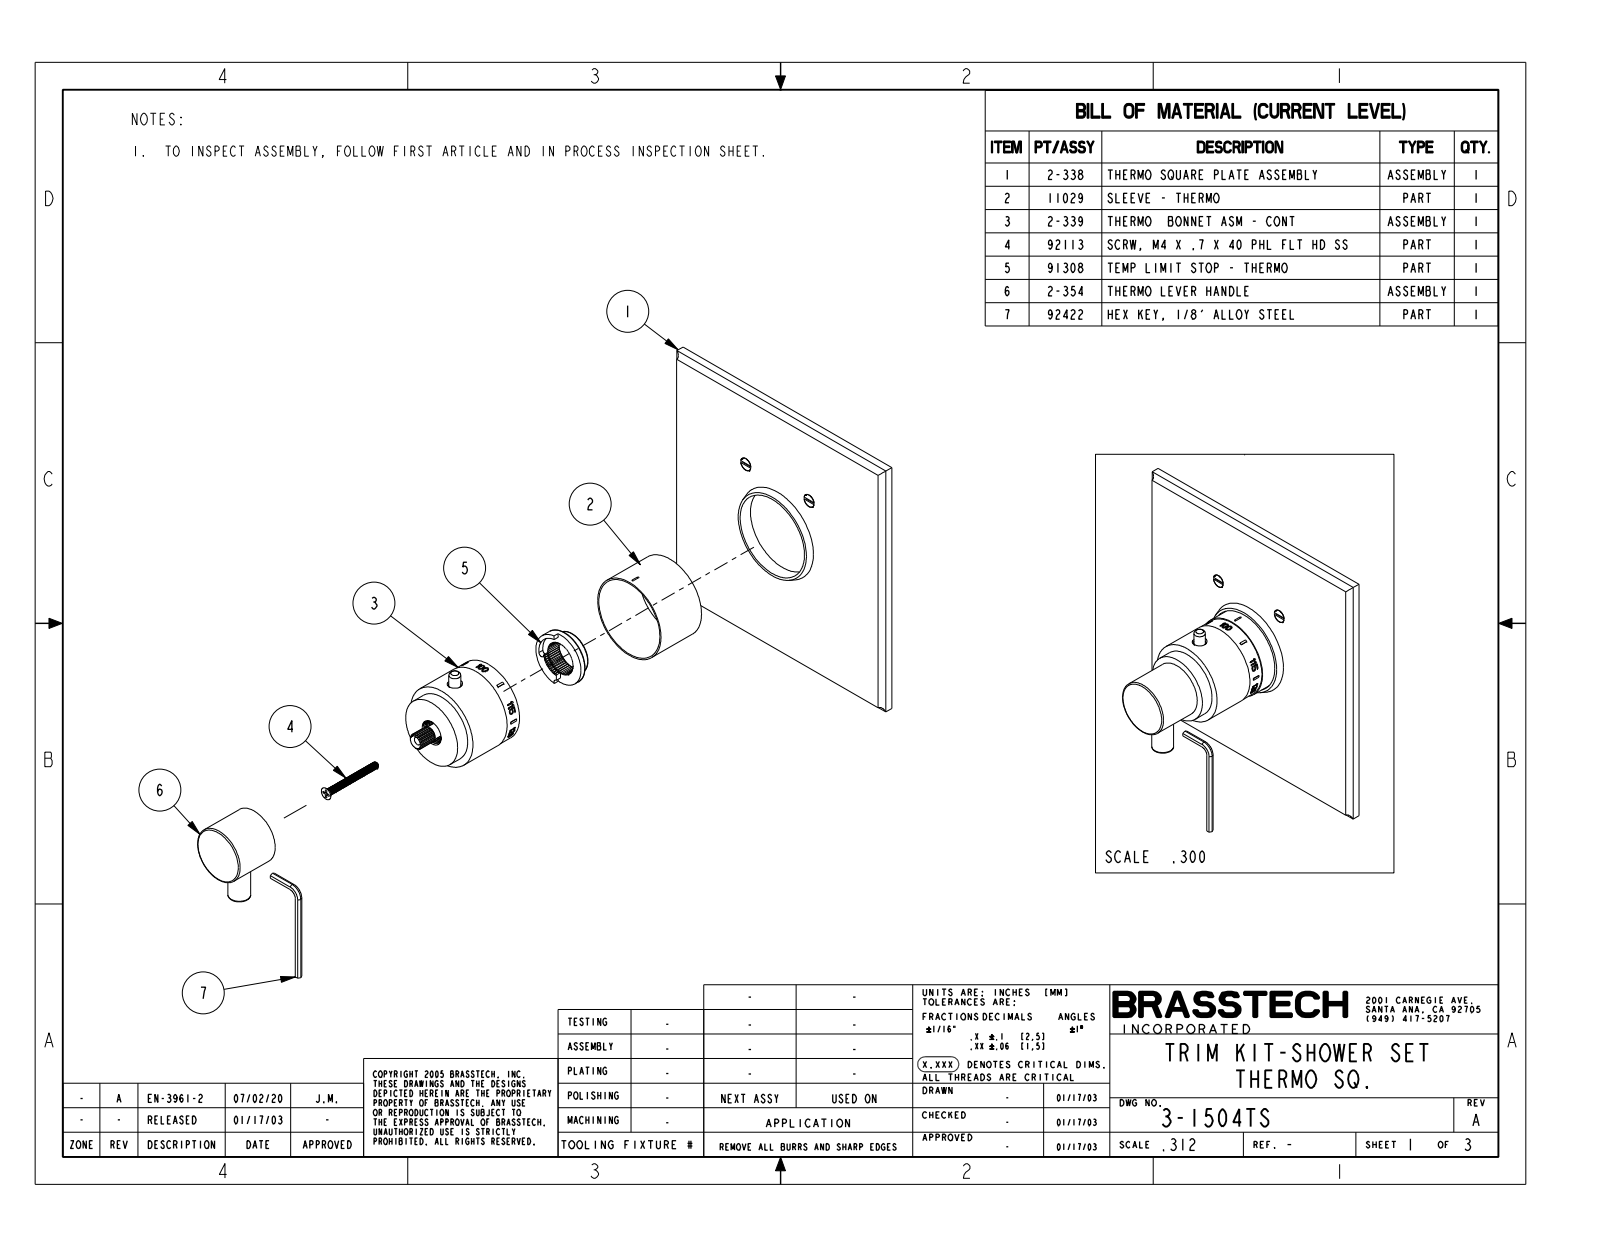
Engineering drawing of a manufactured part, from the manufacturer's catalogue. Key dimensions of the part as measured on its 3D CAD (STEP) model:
Part name (STEP PRODUCT): 3-1504TS
STEP written by: CREO PARAMETRIC BY PTC INC, 2018400 (CONFIG_CONTROL_DESIGN)
Units: inches
Bodies: 1 solid, 405 faces (334 planar, 51 cylindrical, 20 other)
Overall size (bounding box): 6.5 × 6.5 × 3.759
Volume: 21.19 in³ · Surface area: 114 in²
Round holes (diameter × count): ⌀0.196 ×1, ⌀0.25 ×1
Round bosses / shafts (diameter × count): ⌀1.97 ×1, ⌀1.94 ×1, ⌀1.929 ×1, ⌀1.615 ×1, ⌀1.312 ×1, ⌀0.5 ×1, ⌀0.4 ×1, ⌀0.26 ×1
Partial cylindrical surfaces — rounded edges, fillets, slot ends (radius × count): R0.125 ×4, R0.969 ×1
Main face-to-face distances: 0.313, 6.5, 2.623, 2.31, 3.759, 3.446, 1.136, 0.016, 2.639, 2.326
